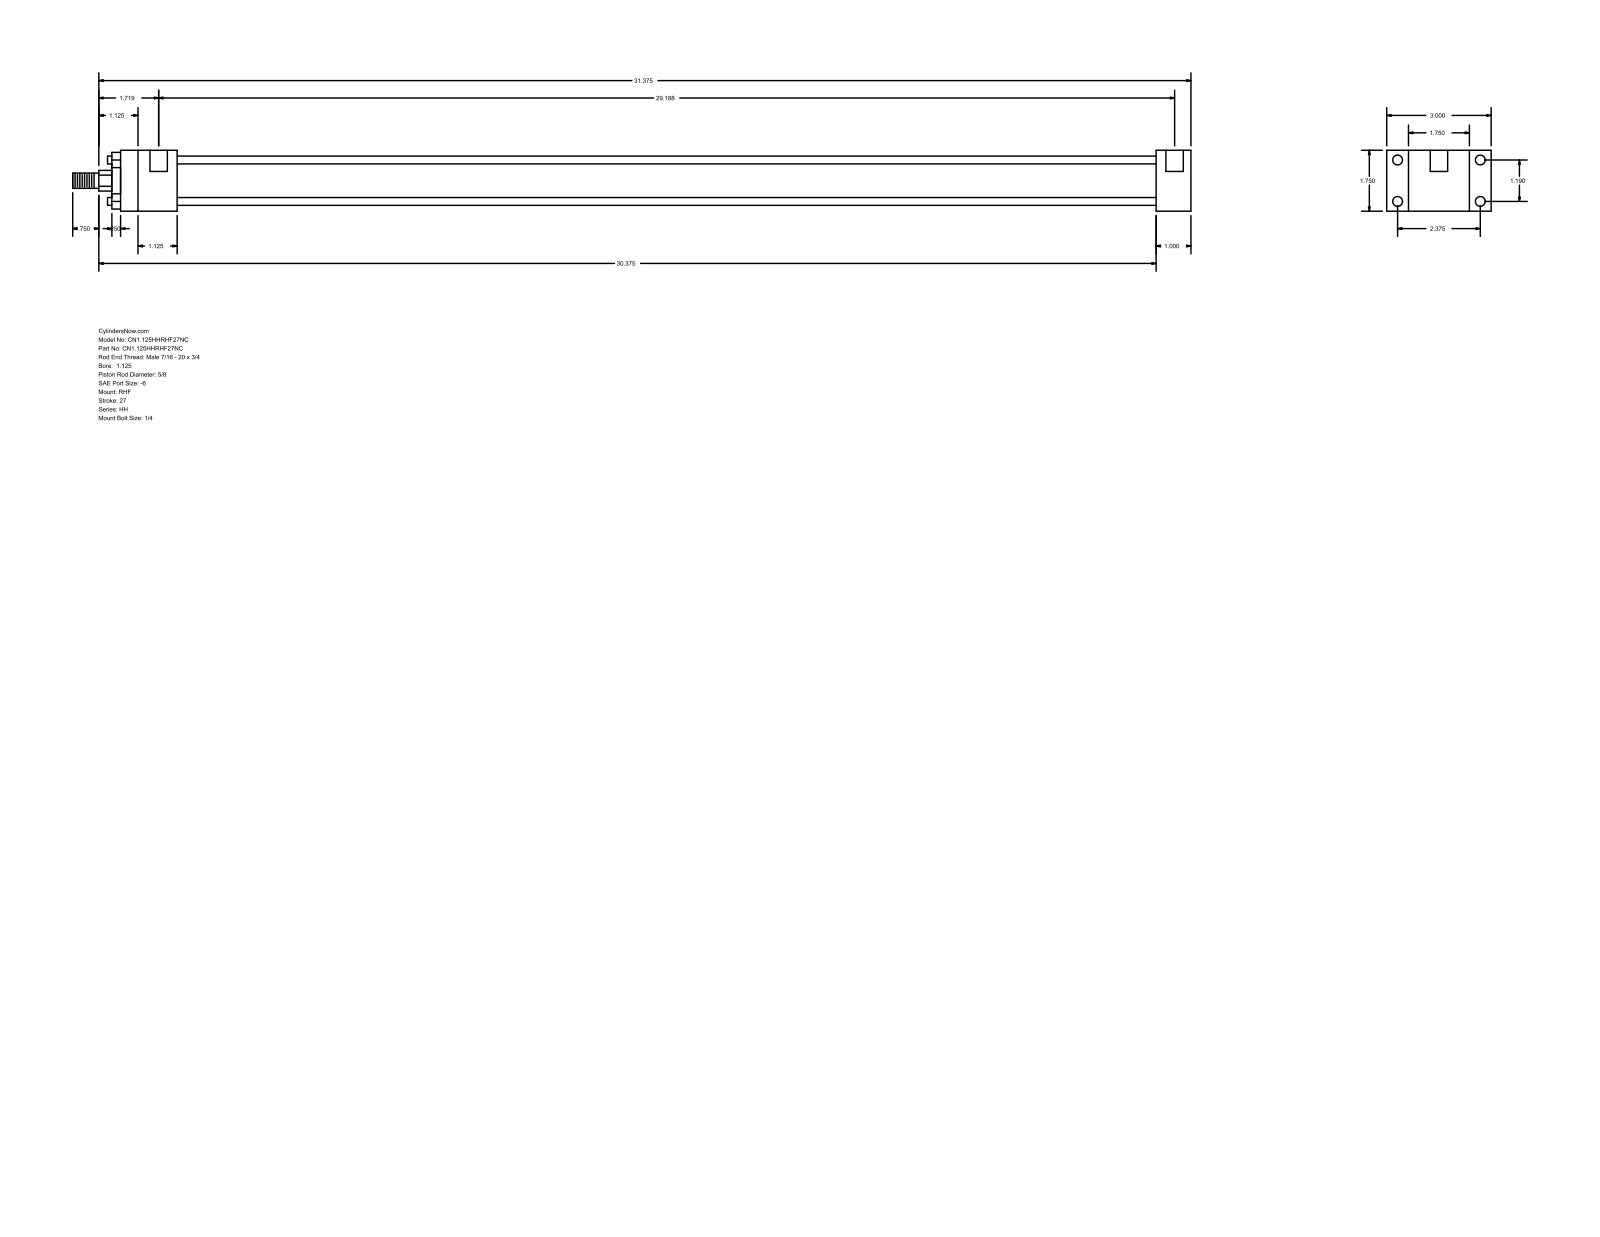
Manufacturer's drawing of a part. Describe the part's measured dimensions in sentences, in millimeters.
The part is named "HH_RHF__0112_0.625". Its 3-D file was written by "GSSL Pune (CONFIG_CONTROL_DESIGN)". It is 0 solids with 88 faces: 60 planar, 28 cylindrical and 0 other. Overall it measures 815.98 by 76.2 by 44.45 millimeters. Round holes: 4 of diameter 5.56, 4 of diameter 7.14, 2 of diameter 12.7. Round bosses or shafts: 4 of diameter 5.71, 1 of diameter 34.92, 1 of diameter 28.57, 1 of diameter 15.88, 1 of diameter 11.11. Partial cylindrical surfaces (rounded edges, fillets, slot ends): 1 of radius 7.54. The main face-to-face distances are 44.46, 15.87, 25.4, 60.33, 76.2, 714.37, 739.77, 41.27, 755.64, 781.04. The hole center spacings are 30.22, 60.32, 67.47, 738.19, 3.17, 741.36.
